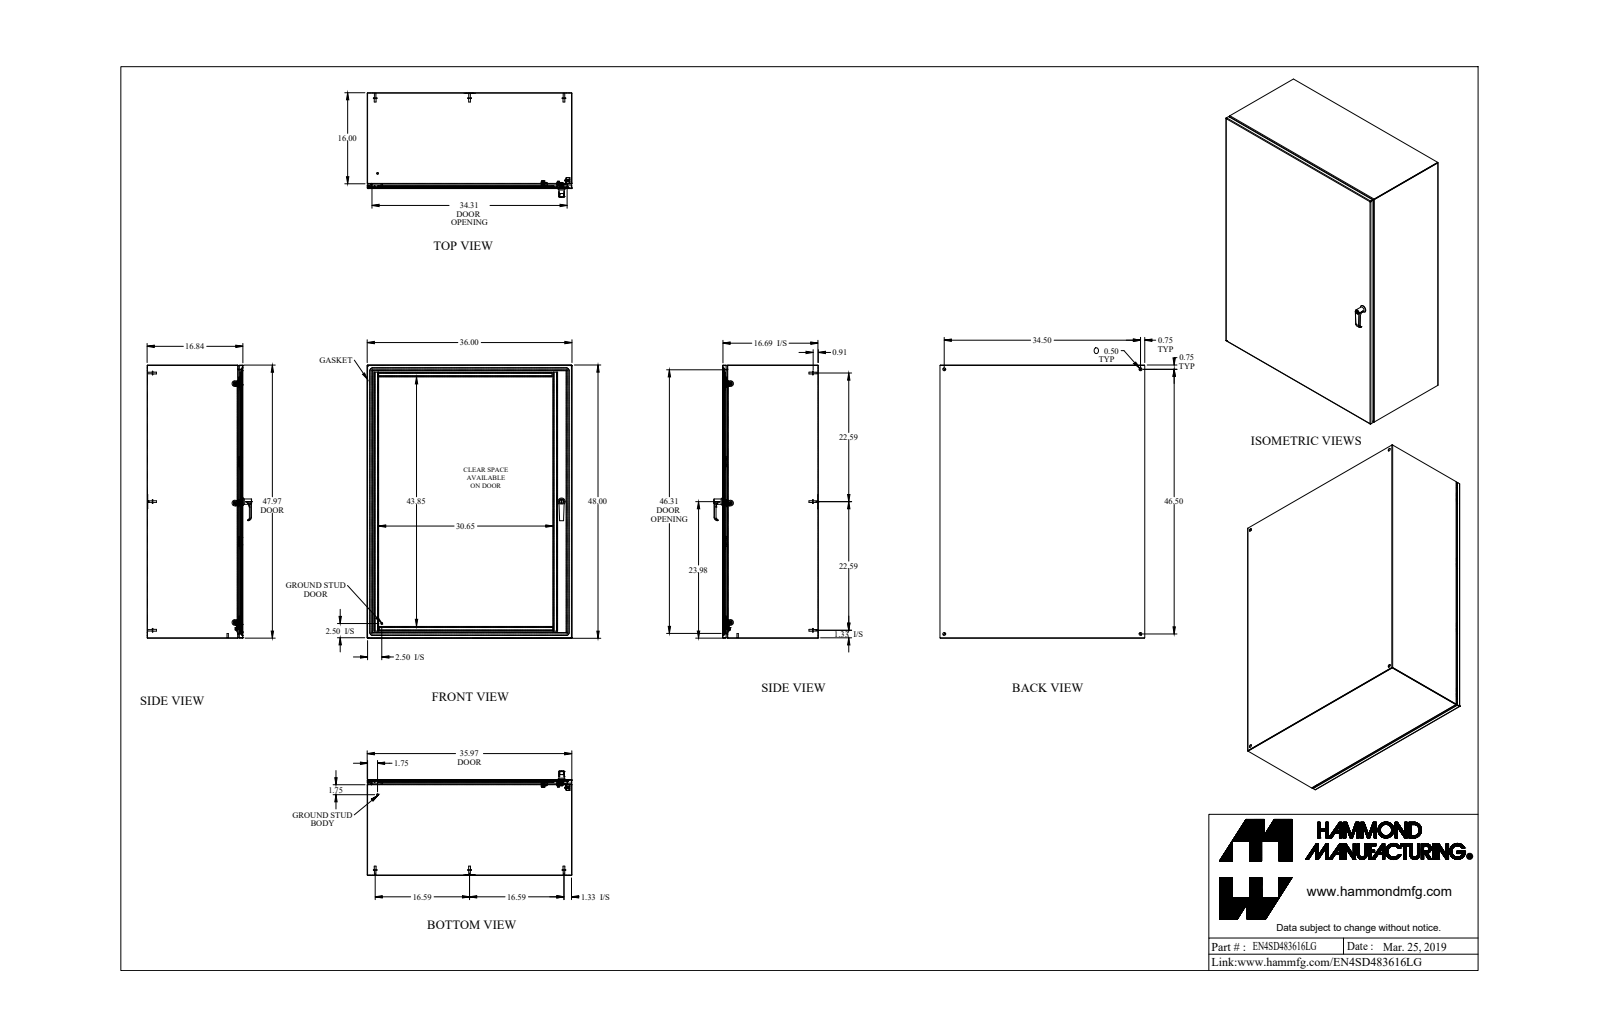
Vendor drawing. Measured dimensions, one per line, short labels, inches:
name: EN4SD483616LG
written by: SolidWorks 2018 (AUTOMOTIVE_DESIGN)
unit: in
bodies: 63 solids, 1719 faces (757 planar, 632 cylindrical, 330 other)
size: 48 × 36 × 18.367
volume: 502.9 in³; area: 14 066 in²
holes: 6× ⌀0.176, 4× ⌀0.196, 4× ⌀0.5, 3× ⌀0.25, 3× ⌀0.265, 3× ⌀0.413, 2× ⌀0.256, 2× ⌀0.313, 2× ⌀0.394, 1× ⌀0.172, 1× ⌀0.24, 1× ⌀0.242
bosses: 8× ⌀0.313, 8× ⌀0.27, 7× ⌀0.25, 6× ⌀0.625, 6× ⌀0.375, 6× ⌀0.156, 3× ⌀1, 3× ⌀0.625
rounds: 24× R0.043, 24× R0.081, 18× R0.036, 18× R0.108, 17× R0.062, 15× R0.03, 10× R0.094, 9× R0.016
face distances: 0.072, 16.765, 16.693, 16.837, 35.928, 35.856, 36, 0.072, 47.856, 47.928
hole spacings: 41.969, 0.787, 20.981, 20.988, 21, 33.504, 34.5, 46.5
